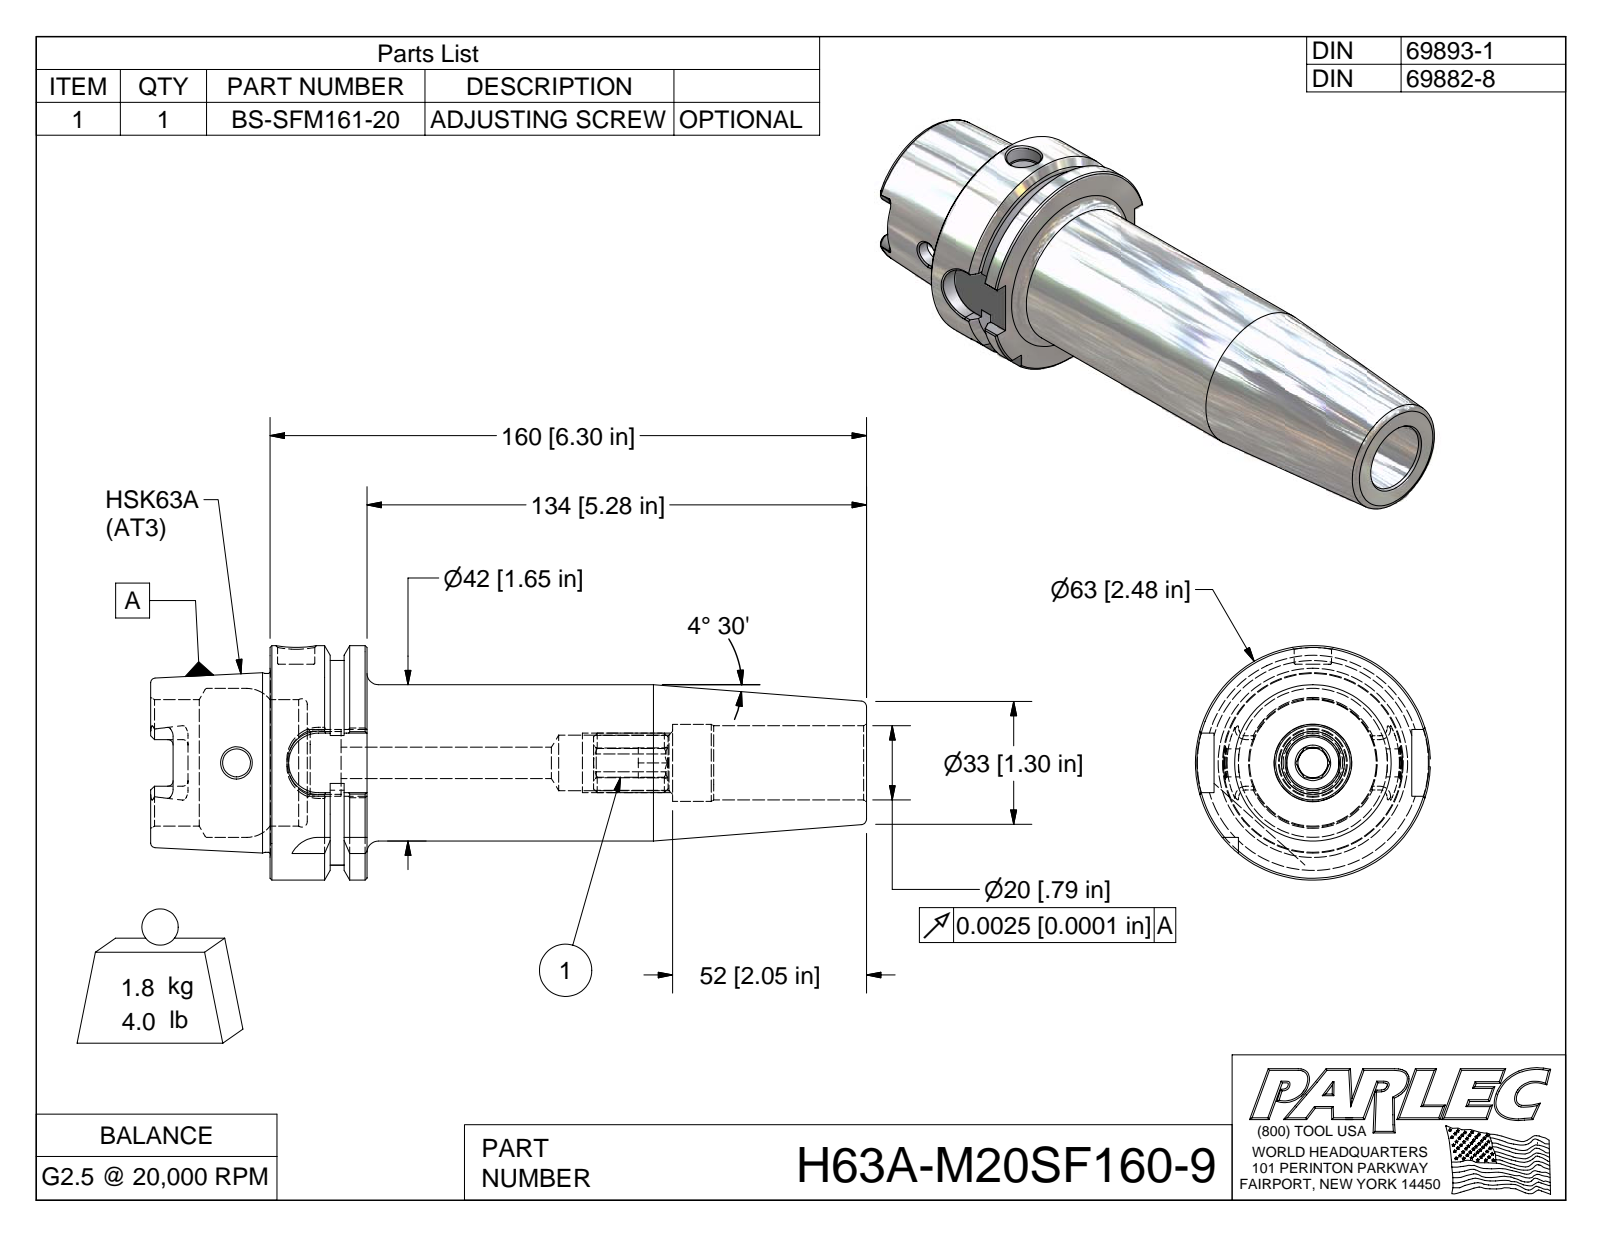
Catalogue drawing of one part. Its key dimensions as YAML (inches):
part_name: "H63A-M20SF160-9; H63A-M20SF160-9-1; BS-SFM161-20"
step_written_by: "Autodesk Inventor 2009 (AUTOMOTIVE_DESIGN)"
units: inches
bodies: {solids: 2, faces: 157, planar: 58, cylindrical: 35, other: 64}
overall_size: [7.559, 2.48, 2.48]
volume: 14.01
surface_area: 71.6
round_holes:
  - {diameter: 0.295, count: 1}
  - {diameter: 0.394, count: 1}
  - {diameter: 0.666, count: 1}
  - {diameter: 0.786, count: 1}
  - {diameter: 0.816, count: 1}
  - {diameter: 1.339, count: 1}
  - {diameter: 1.575, count: 1}
round_bosses_or_shafts:
  - {diameter: 2.48, count: 1}
  - {diameter: 1.891, count: 1}
  - {diameter: 1.654, count: 1}
partial_cylinders:
  - {radius: 0.059, count: 6}
  - {radius: 0.315, count: 5}
  - {radius: 0.113, count: 4}
  - {radius: 1.083, count: 1}
face_to_face_distances: [1.024, 0.241, 0.389, 0.394, 0.63, 5.276, 1.26, 6.299, 5.906, 1.654]
